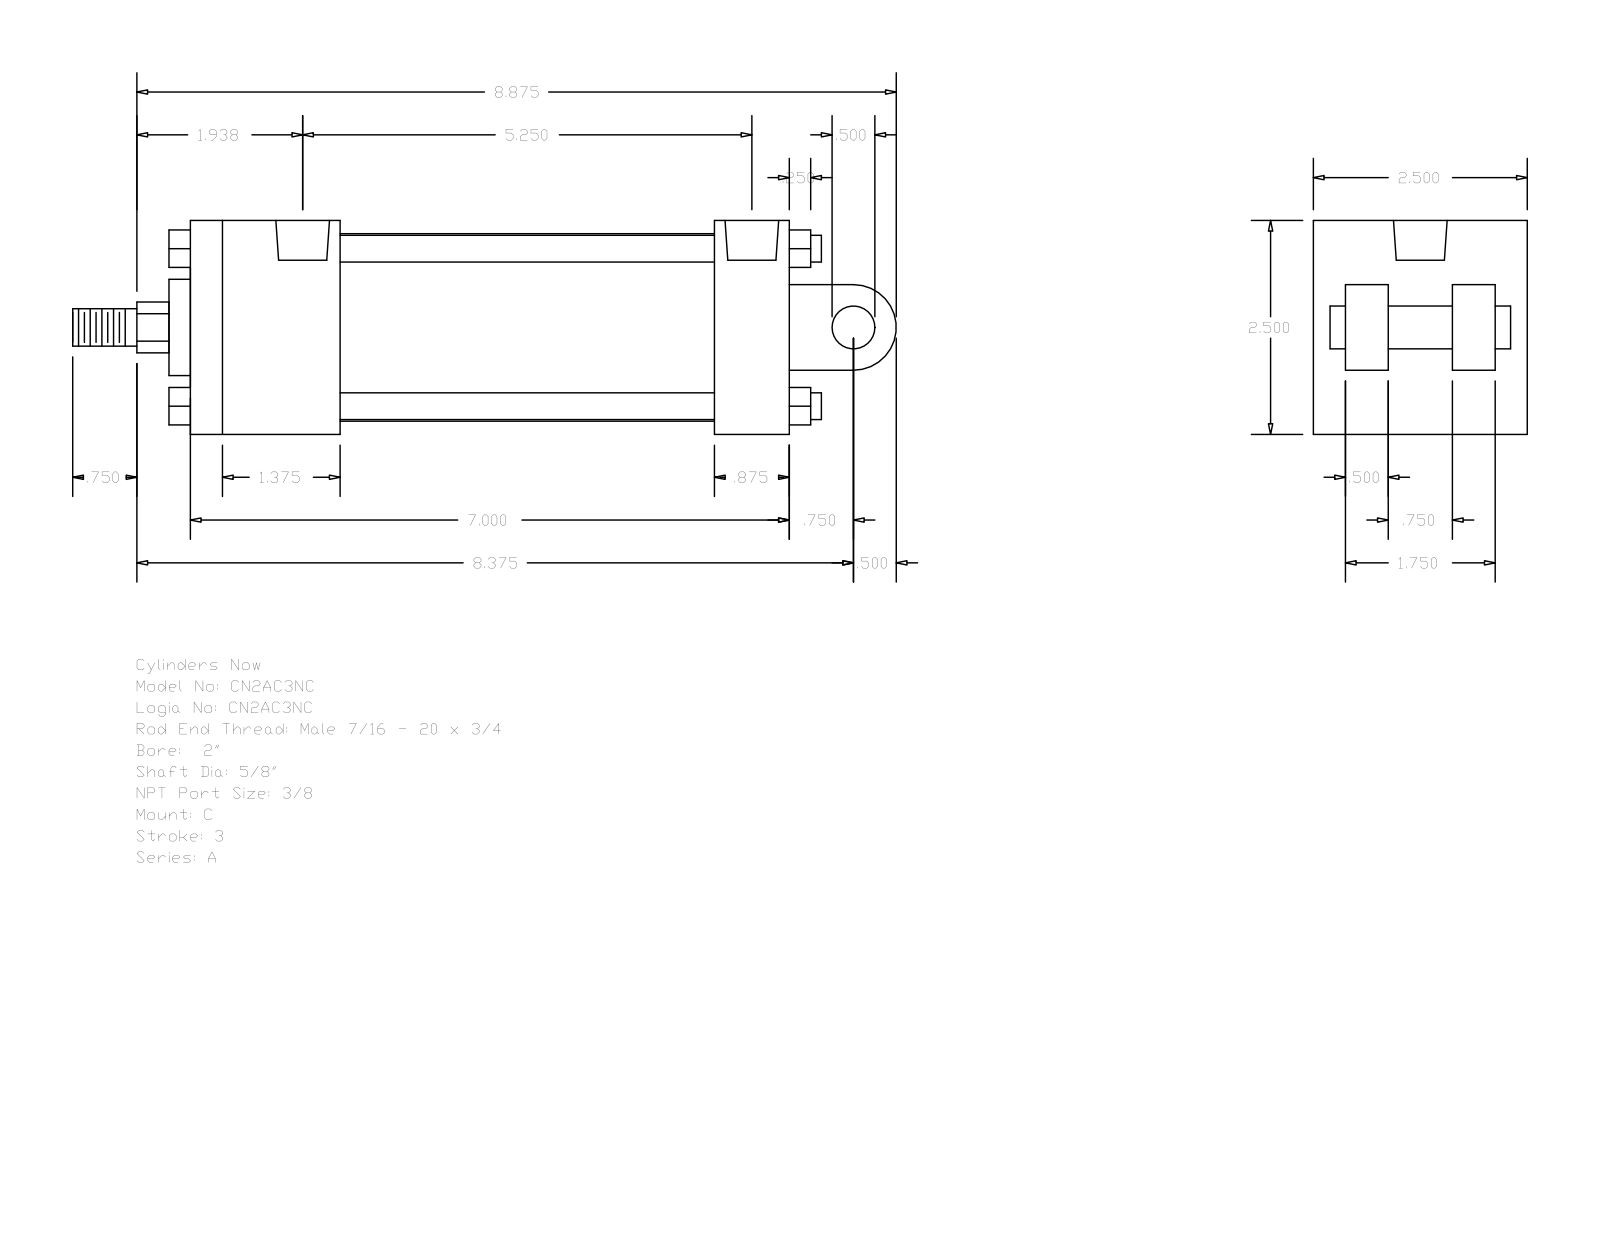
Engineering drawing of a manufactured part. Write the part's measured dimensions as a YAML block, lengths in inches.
part_name: "A_C__0200_0.625"
step_written_by: "GSSL Pune (CONFIG_CONTROL_DESIGN)"
units: inches
bodies: {solids: 0, faces: 135, planar: 102, cylindrical: 33, other: 0}
overall_size: [9.625, 2.5, 2.5]
round_holes:
  - {diameter: 0.219, count: 4}
  - {diameter: 0.627, count: 2}
round_bosses_or_shafts:
  - {diameter: 0.313, count: 4}
  - {diameter: 2.19, count: 1}
  - {diameter: 1.125, count: 1}
  - {diameter: 0.625, count: 1}
  - {diameter: 0.5, count: 1}
  - {diameter: 0.437, count: 1}
partial_cylinders:
  - {radius: 0.297, count: 1}
  - {radius: 0.5, count: 1}
face_to_face_distances: [2.5, 7, 1.75, 0.375, 5.25, 6.125, 4.375, 0.875, 0.5, 0.25]
hole_center_spacings: [4.937, 0.156, 0.157, 5.093, 5.094, 5.25]
